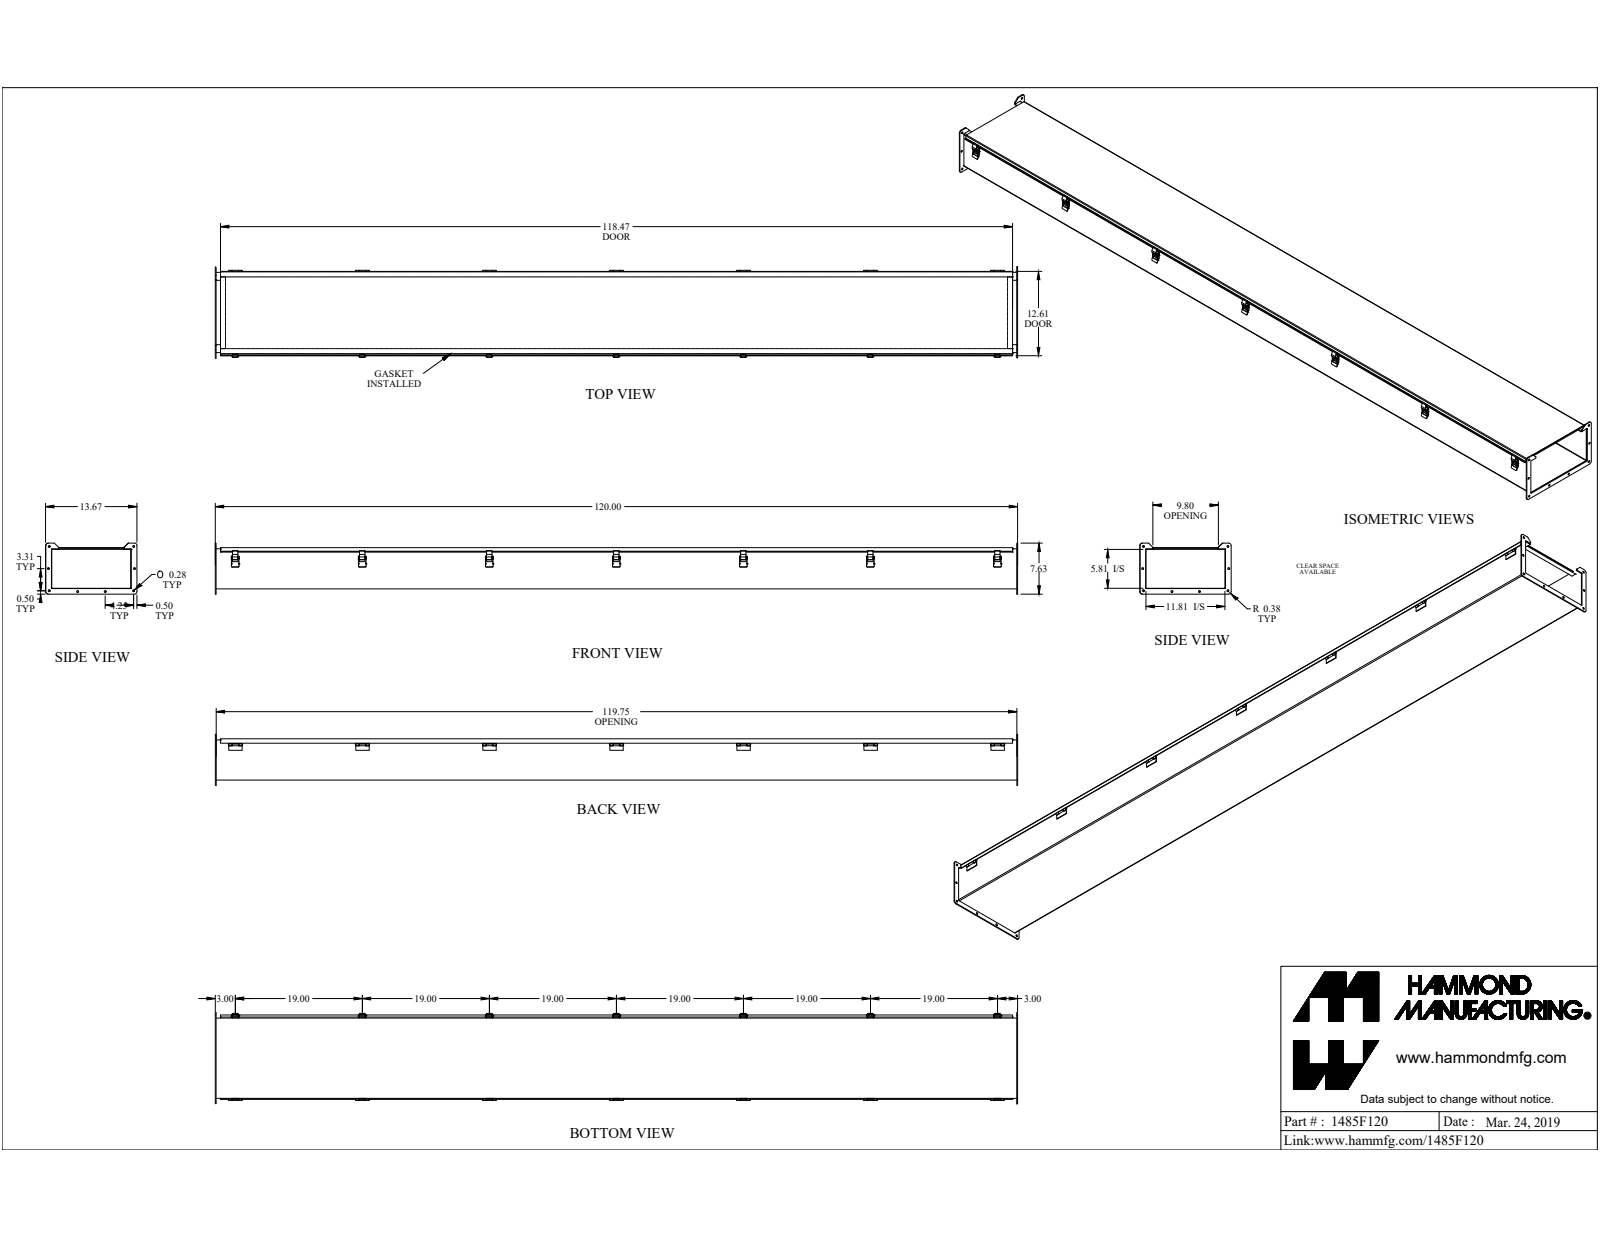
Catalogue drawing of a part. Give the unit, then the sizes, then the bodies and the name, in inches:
Units: inches
Overall size (bounding box): 120 × 13.67 × 7.625
Round holes (diameter × count): ⌀0.281 ×16, ⌀0.125 ×1, ⌀0.13 ×1, ⌀0.164 ×1
Round bosses / shafts (diameter × count): ⌀0.187 ×2, ⌀0.275 ×1, ⌀0.156 ×1, ⌀0.125 ×1, ⌀0.125 ×1
Partial cylindrical surfaces — rounded edges, fillets, slot ends (radius × count): R0.016 ×43, R0.125 ×23, R0.035 ×15, R0.039 ×15, R0.076 ×15, R0.015 ×14, R0.029 ×14, R0.086 ×14
Main face-to-face distances: 0.095, 0.072, 6.1, 6.172, 6.005, 6.077, 11.905, 12, 11.81, 5.905
Hole centre spacings: 0.045, 3.315, 6.625, 13.173, 3.313, 3.317, 4.252, 5.564
Volume: 456.7 in³ · Surface area: 10 212 in²
Bodies: 50 solids, 1143 faces (670 planar, 459 cylindrical, 14 other)
Part name (STEP PRODUCT): 1485F120
STEP written by: SolidWorks 2019 (CONFIG_CONTROL_DESIGN)
